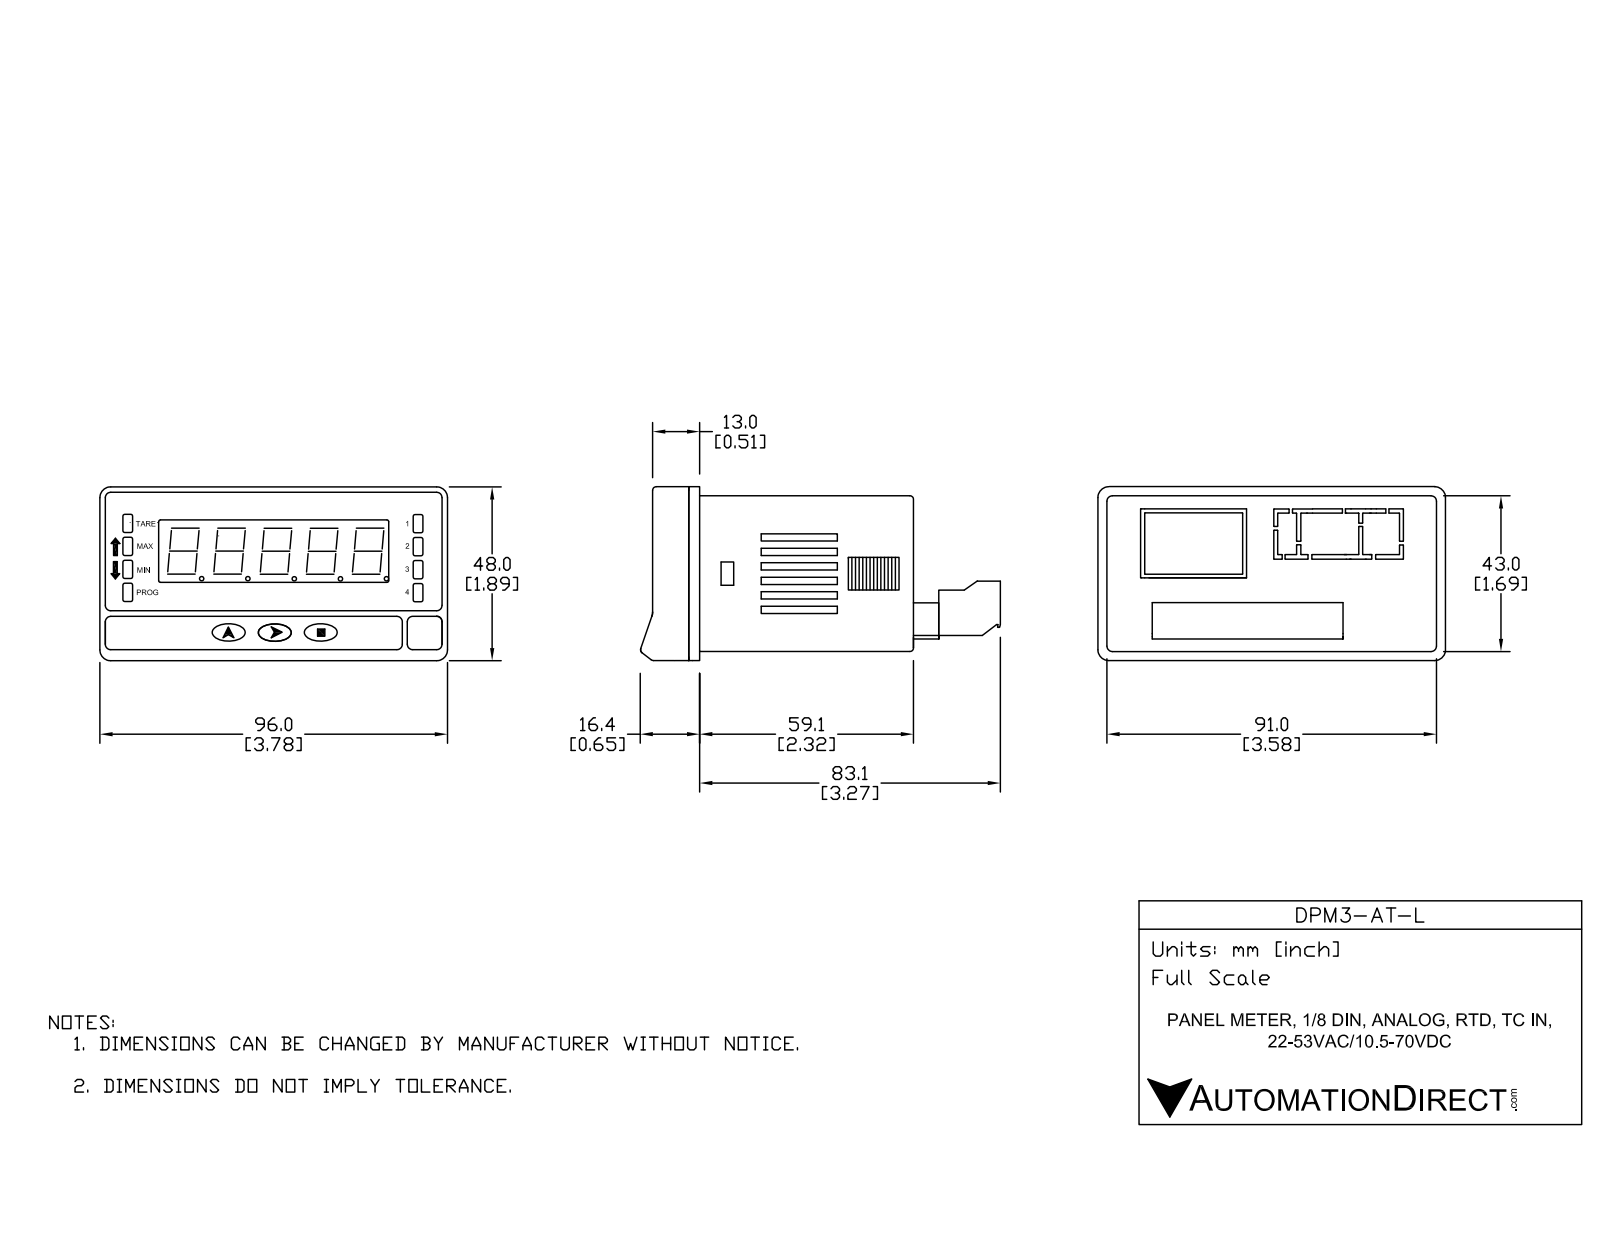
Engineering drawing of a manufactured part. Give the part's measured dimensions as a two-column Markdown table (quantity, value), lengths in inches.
| quantity | value |
| --- | --- |
| part name | DPM3-AT-L |
| STEP written by | SolidWorks 2017 (AUTOMOTIVE_DESIGN) |
| units | inches |
| bodies | 10 solids, 2622 faces (2041 planar, 368 cylindrical, 213 other) |
| overall size | 3.916 × 3.78 × 1.89 |
| volume | 5.643 in³ |
| surface area | 104.7 in² |
| round holes (diameter × count) | 0.039 × 12, 0.079 × 12, 0.078 × 10, 0.118 × 10, 0.152 × 10 |
| round bosses / shafts (diameter × count) | 0.047 × 5 |
| partial cylindrical surfaces (radius × count) | 0.004 × 53, 0.02 × 42, 0.012 × 24, 0.014 × 24, 0.07 × 12, 0.072 × 12, 0.118 × 10, 0.121 × 10 |
| main face-to-face distances | 0.059, 1.634, 0.098, 1.693, 1.575, 1.732, 3.524, 0.433, 0.157, 2.78 |
| hole center spacings | 0.138, 0.276, 0.201, 0.413, 0.748, 0.197, 0.197, 0.201 |
